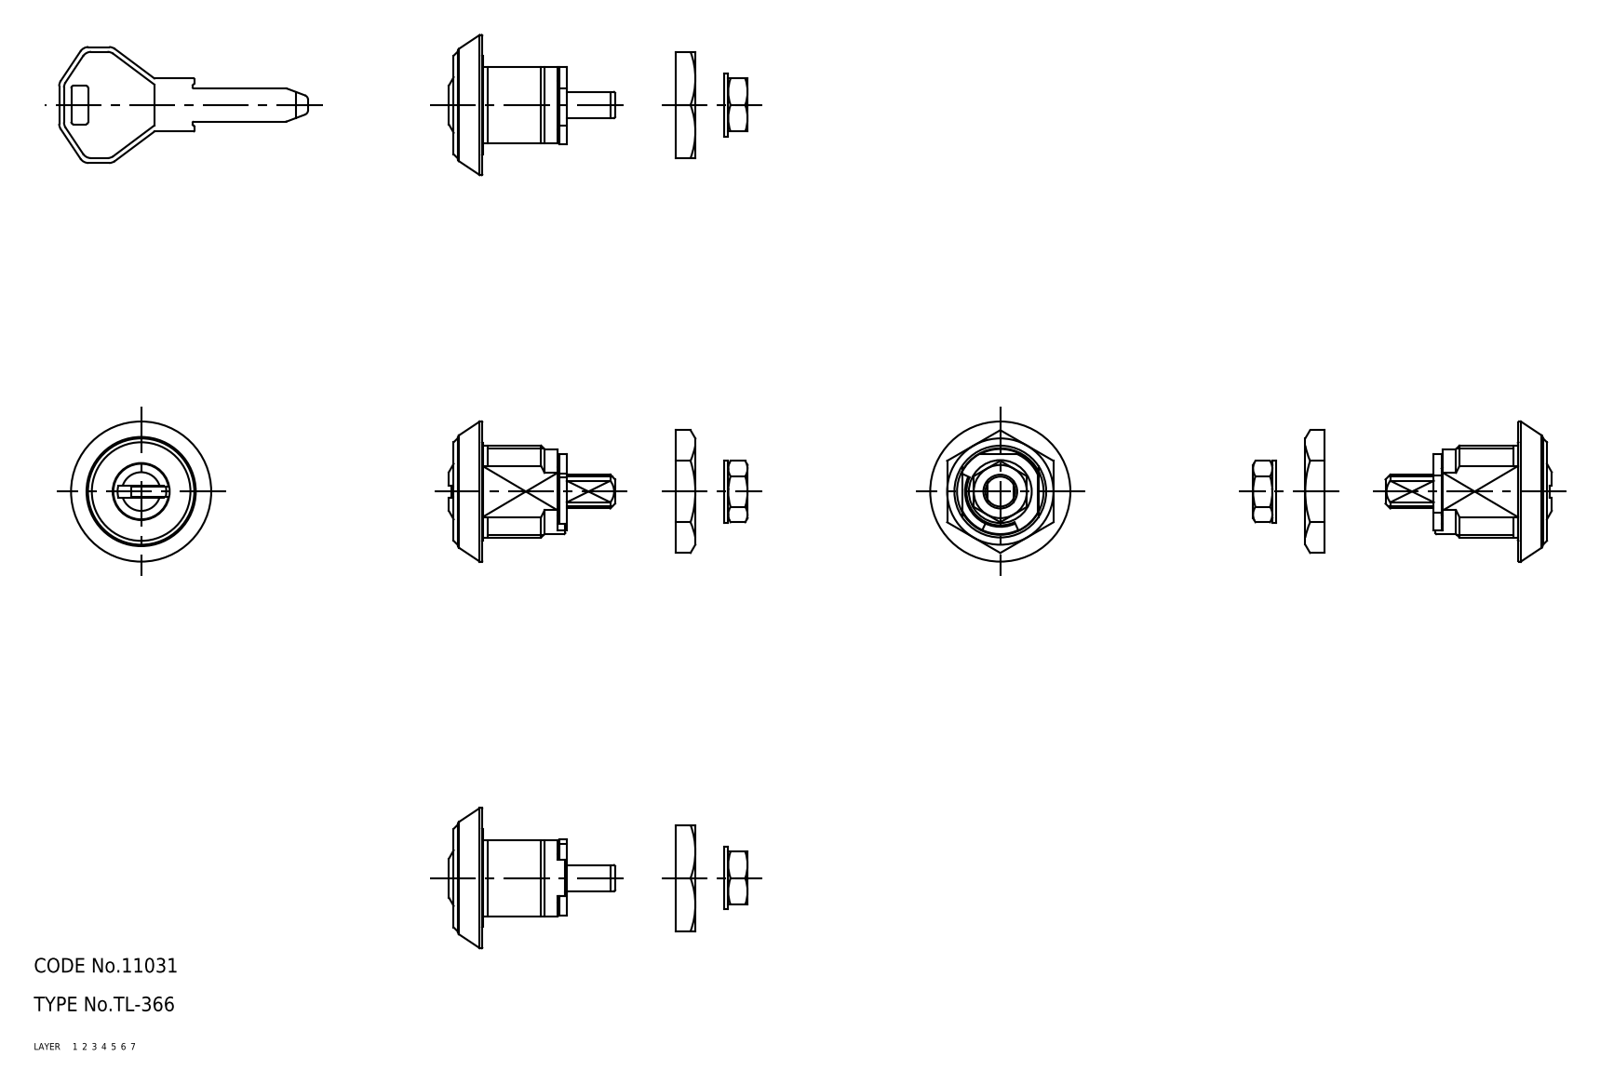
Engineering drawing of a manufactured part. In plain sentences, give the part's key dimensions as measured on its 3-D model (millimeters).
The part is named "67118285; 67118298; 67118311; 67118324 (+2 more)". Its 3-D file was written by "CADfix (AUTOMOTIVE_DESIGN)". It is 6 solids with 209 faces: 0 planar, 0 cylindrical and 209 other. Overall it measures 123.8 by 29 by 29 millimeters. Its volume is 9 712 cubic millimeters and its surface area 6 322 square millimeters.
